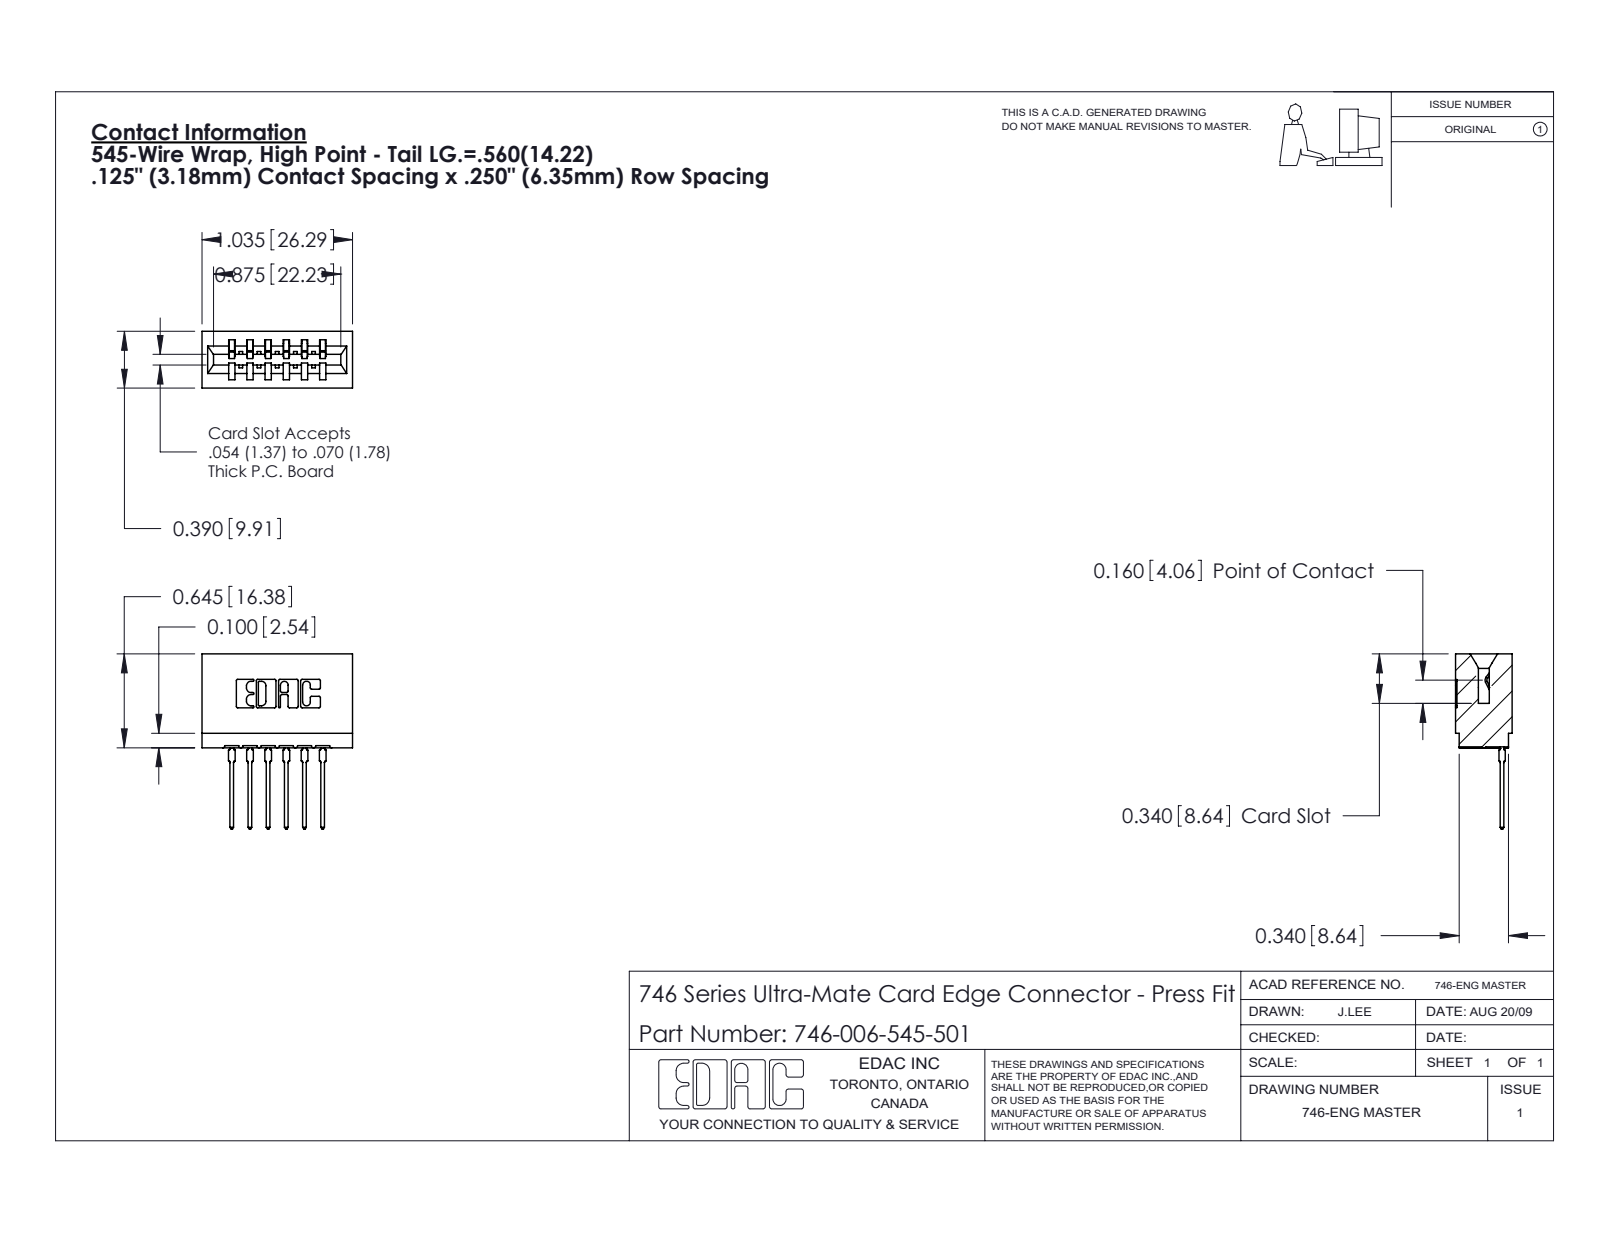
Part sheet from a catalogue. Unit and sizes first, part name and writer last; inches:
Units: inches
Overall size (bounding box): 1.204 × 1.035 × 0.39
Partial cylindrical surfaces — rounded edges, fillets, slot ends (radius × count): R0.01 ×22, R0.021 ×12, R0.015 ×7, R0.007 ×6, R0.031 ×6, R0.005 ×4, R0.011 ×4, R0.026 ×3
Main face-to-face distances: 0.25, 0.125, 0.042, 0.333, 0.057, 0.375, 0.39, 0.292, 0.5, 0.208
Volume: 0.195 in³ · Surface area: 5.945 in²
Bodies: 7 solids, 745 faces (433 planar, 156 cylindrical, 156 other)
Part name (STEP PRODUCT): 746-006-545-501; 746-292-001_545; 746 Part_.340 Slot Depth - 01
STEP written by: SolidWorks 2020 (CONFIG_CONTROL_DESIGN)
